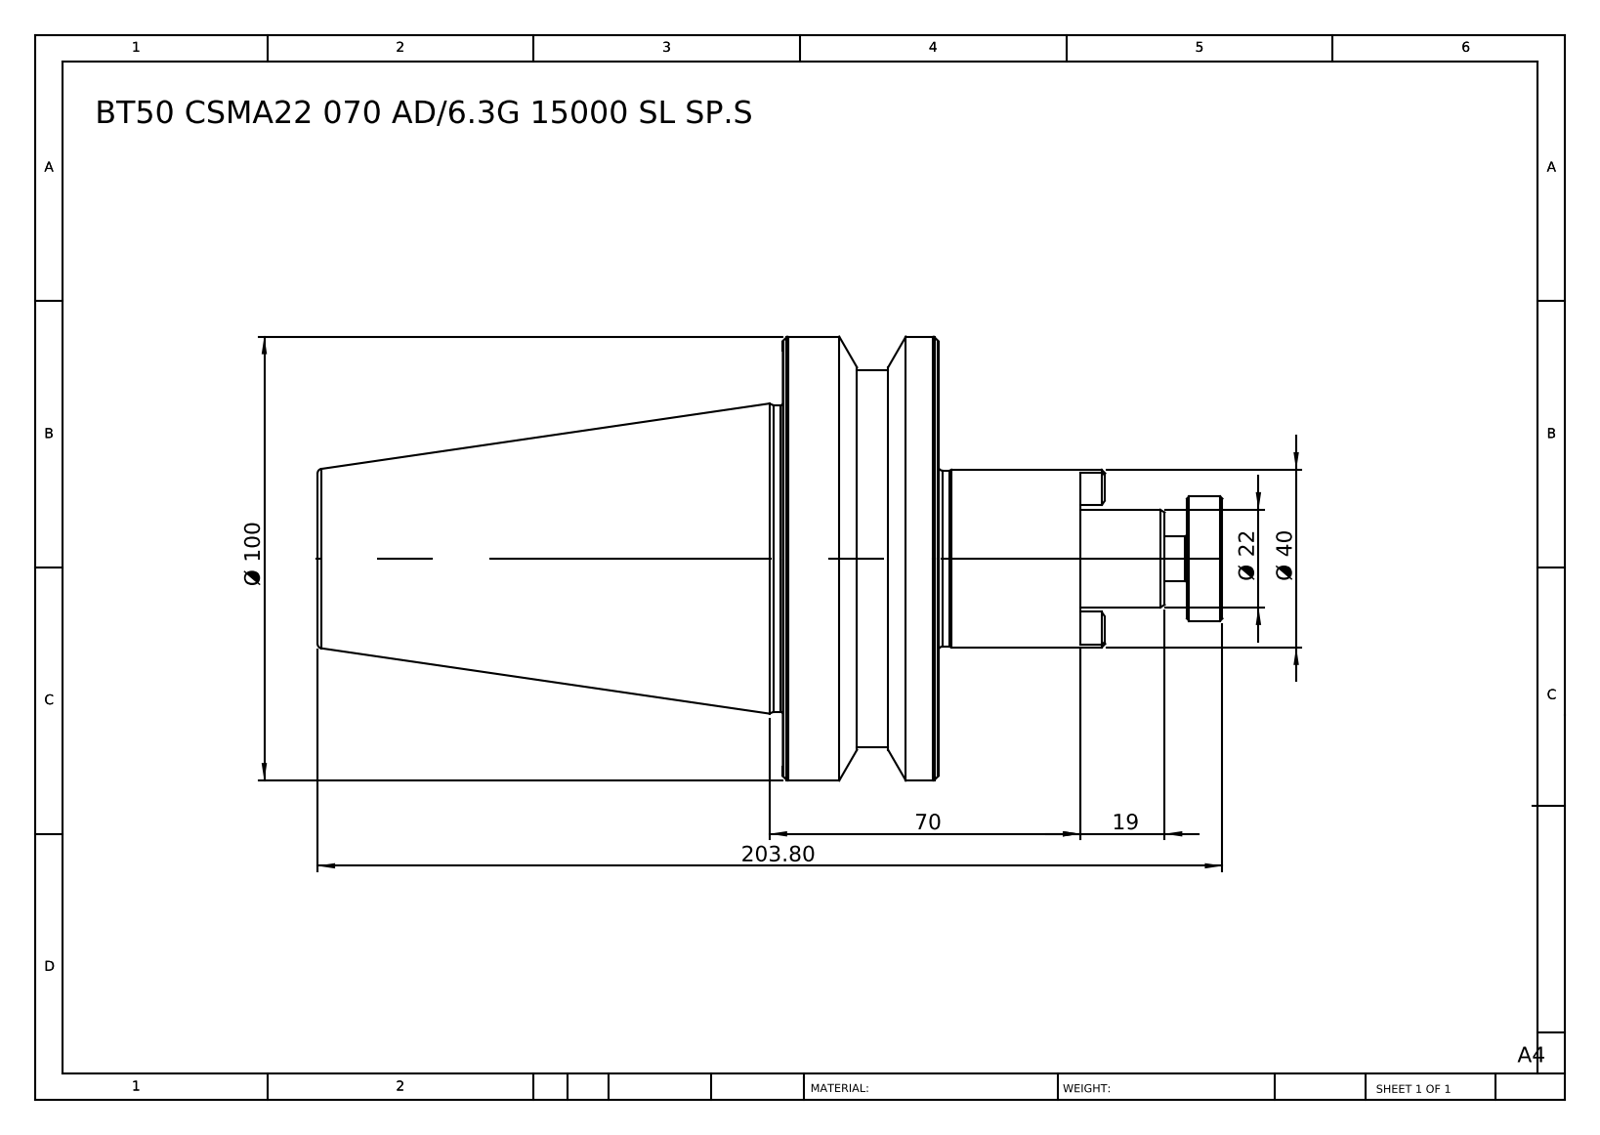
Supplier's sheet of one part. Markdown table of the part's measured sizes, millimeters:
| quantity | value |
| --- | --- |
| part name | BT50 CSMA22 070 AD-6.3G 15000 SL SP.S |
| STEP written by | SolidWorks 2014 (CONFIG_CONTROL_DESIGN) |
| units | millimeters |
| bodies | 1 solid, 79 faces (19 planar, 20 cylindrical, 40 other) |
| overall size | 203.8 × 100 × 100 |
| volume | 563 469 mm³ |
| surface area | 51 856 mm² |
| round bosses / shafts (diameter × count) | 100 × 1, 85 × 1, 69 × 1, 40 × 1, 39.6 × 1, 28 × 1, 22 × 1, 10 × 1 |
| partial cylindrical surfaces (radius × count) | 13 × 1 |
| main face-to-face distances | 35, 32, 139.8, 104.8, 67, 171.8, 64, 99, 203.8, 8 |
